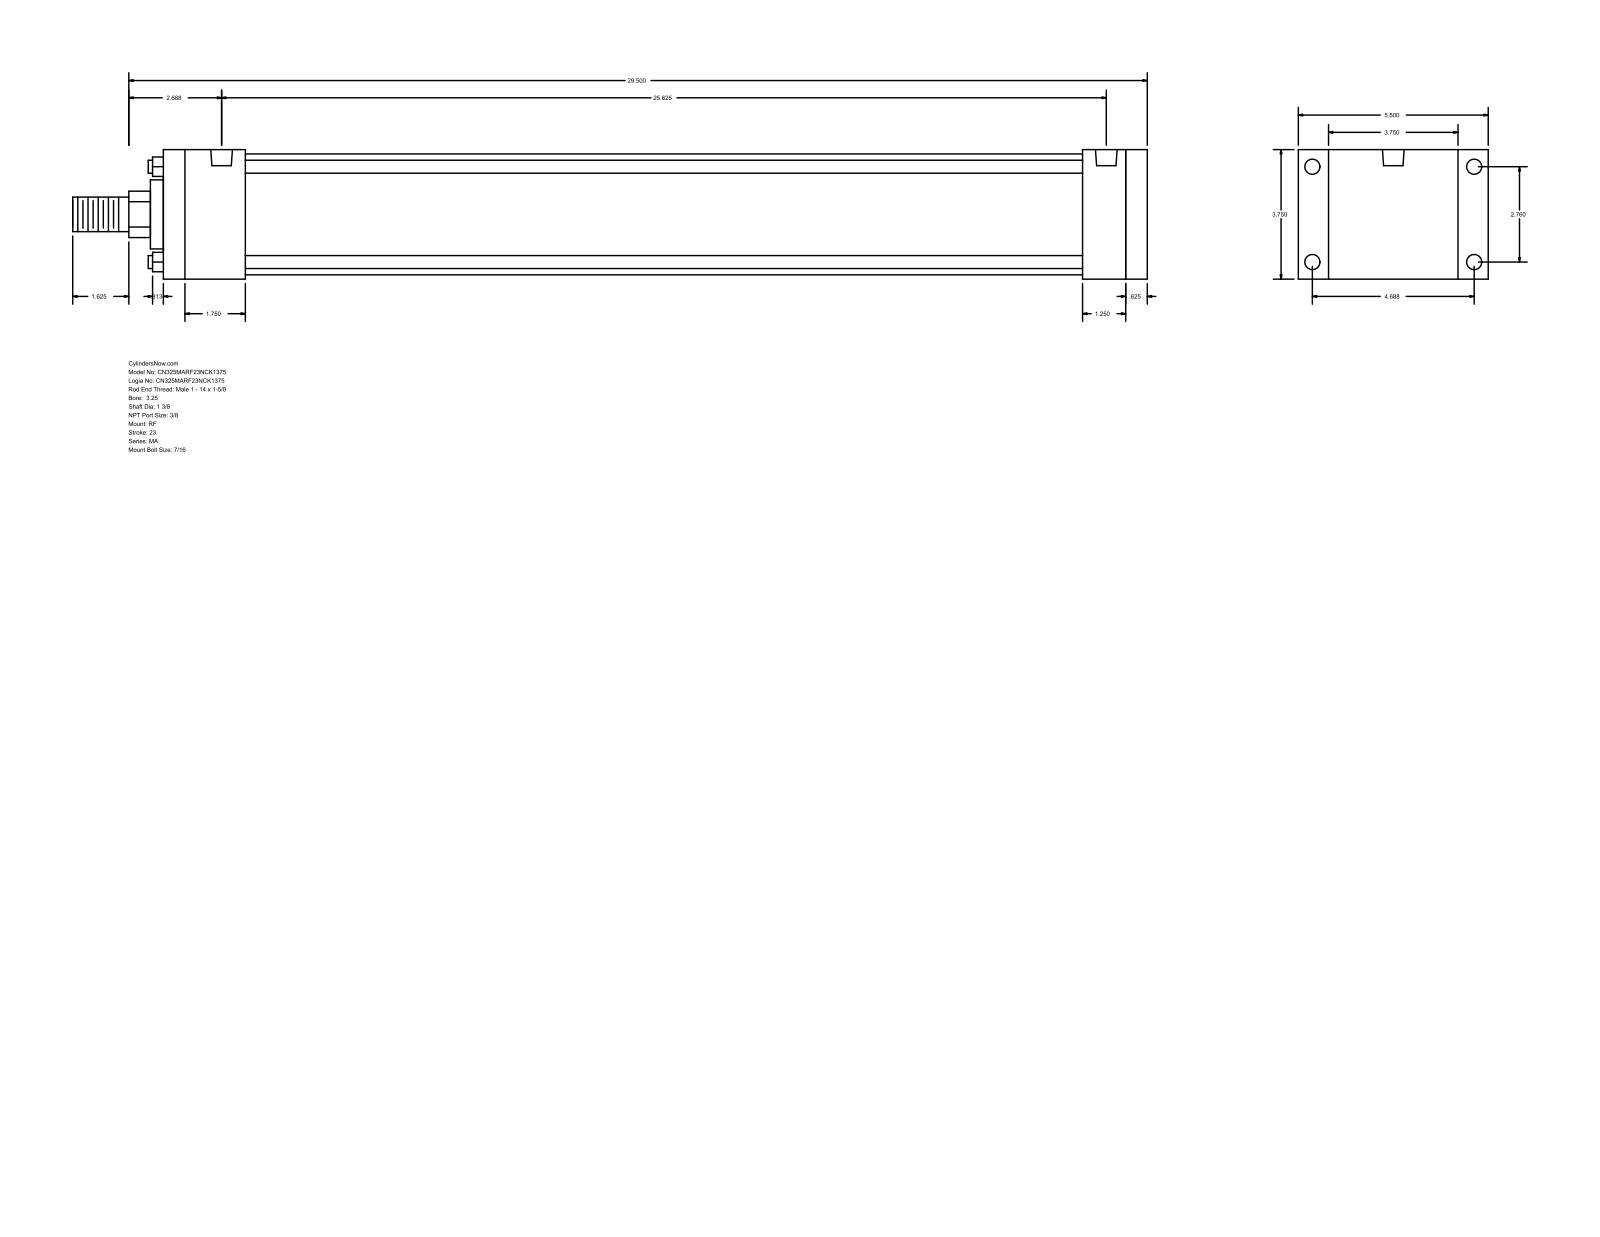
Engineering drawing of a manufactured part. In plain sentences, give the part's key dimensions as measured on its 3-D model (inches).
The part is named "MA_RF__0325_1.375". Its 3-D file was written by "GSSL Pune (CONFIG_CONTROL_DESIGN)". It is 0 solids with 92 faces: 64 planar, 28 cylindrical and 0 other. Overall it measures 31.125 by 5.5 by 3.75 inches. Round holes: 8 of diameter 0.437, 2 of diameter 0.627. Round bosses or shafts: 4 of diameter 0.375, 1 of diameter 3.5, 1 of diameter 2, 1 of diameter 1.375, 1 of diameter 1. Partial cylindrical surfaces (rounded edges, fillets, slot ends): 1 of radius 0.672. The main face-to-face distances are 3.75, 28.5, 0.625, 27.875, 0.875, 4.625, 26.625, 1.25, 1.875, 2.375. The hole center spacings are 2.76, 4.687, 5.439, 25.25, 0.187, 0.188, 25.437, 25.438.
